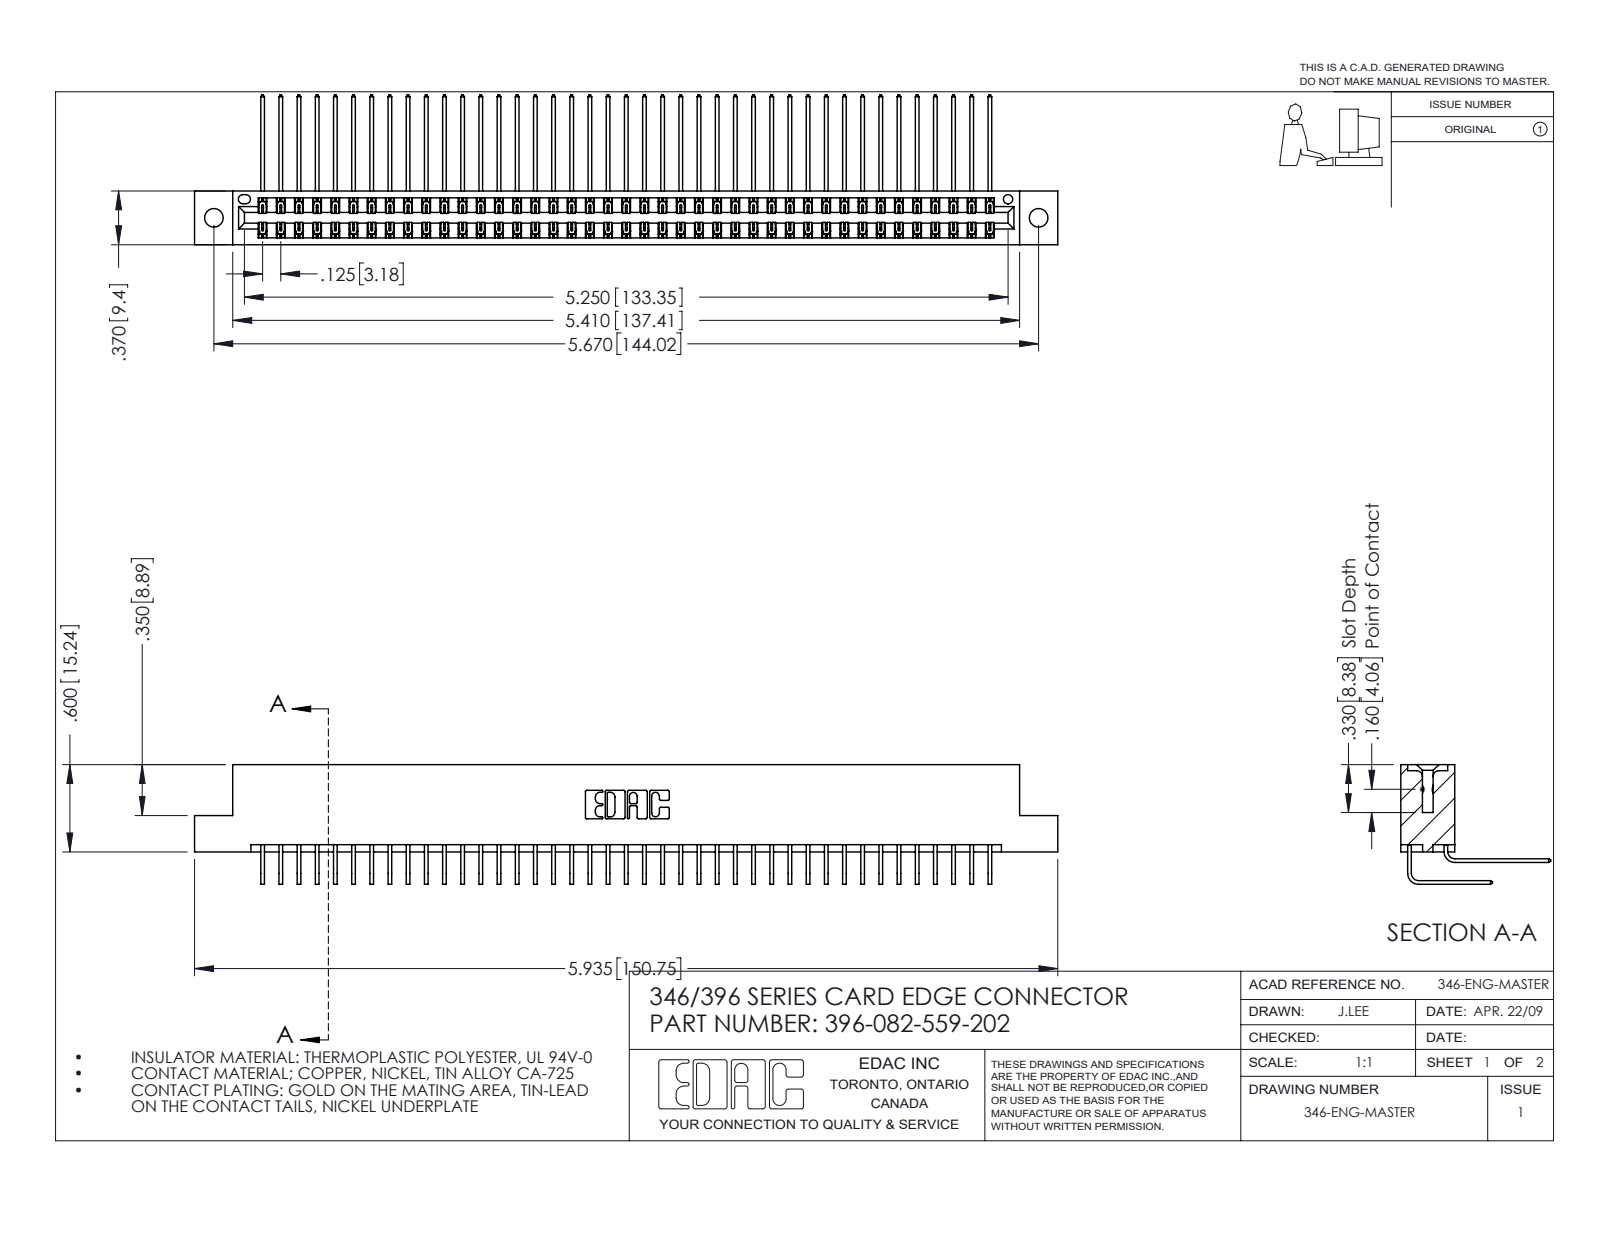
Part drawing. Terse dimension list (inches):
name: 345-292-001_558 559 Tail - 1; 345-292-001_559 Tail - 2; 396-082-559-202; 346 Part_Flush Mounting Lugs - 0.128 Dia
written by: SolidWorks 2016 (CONFIG_CONTROL_DESIGN)
unit: in
bodies: 83 solids, 4550 faces (3110 planar, 1440 cylindrical, 0 other)
size: 5.935 × 1.03 × 0.823
volume: 0.923 in³; area: 35.31 in²
holes: 2× ⌀0.128, 1× ⌀0.064
rounds: 123× R0.006, 22× R0.01, 6× R0.007, 6× R0.031, 3× R0.026, 2× R0.014, 2× R0.022, 2× R0.024
face distances: 0.048, 0.322, 0.025, 0.37, 0.25, 0.072, 0.298, 0.275, 0.148, 0.222
hole spacings: 0.246, 5.461, 5.67
